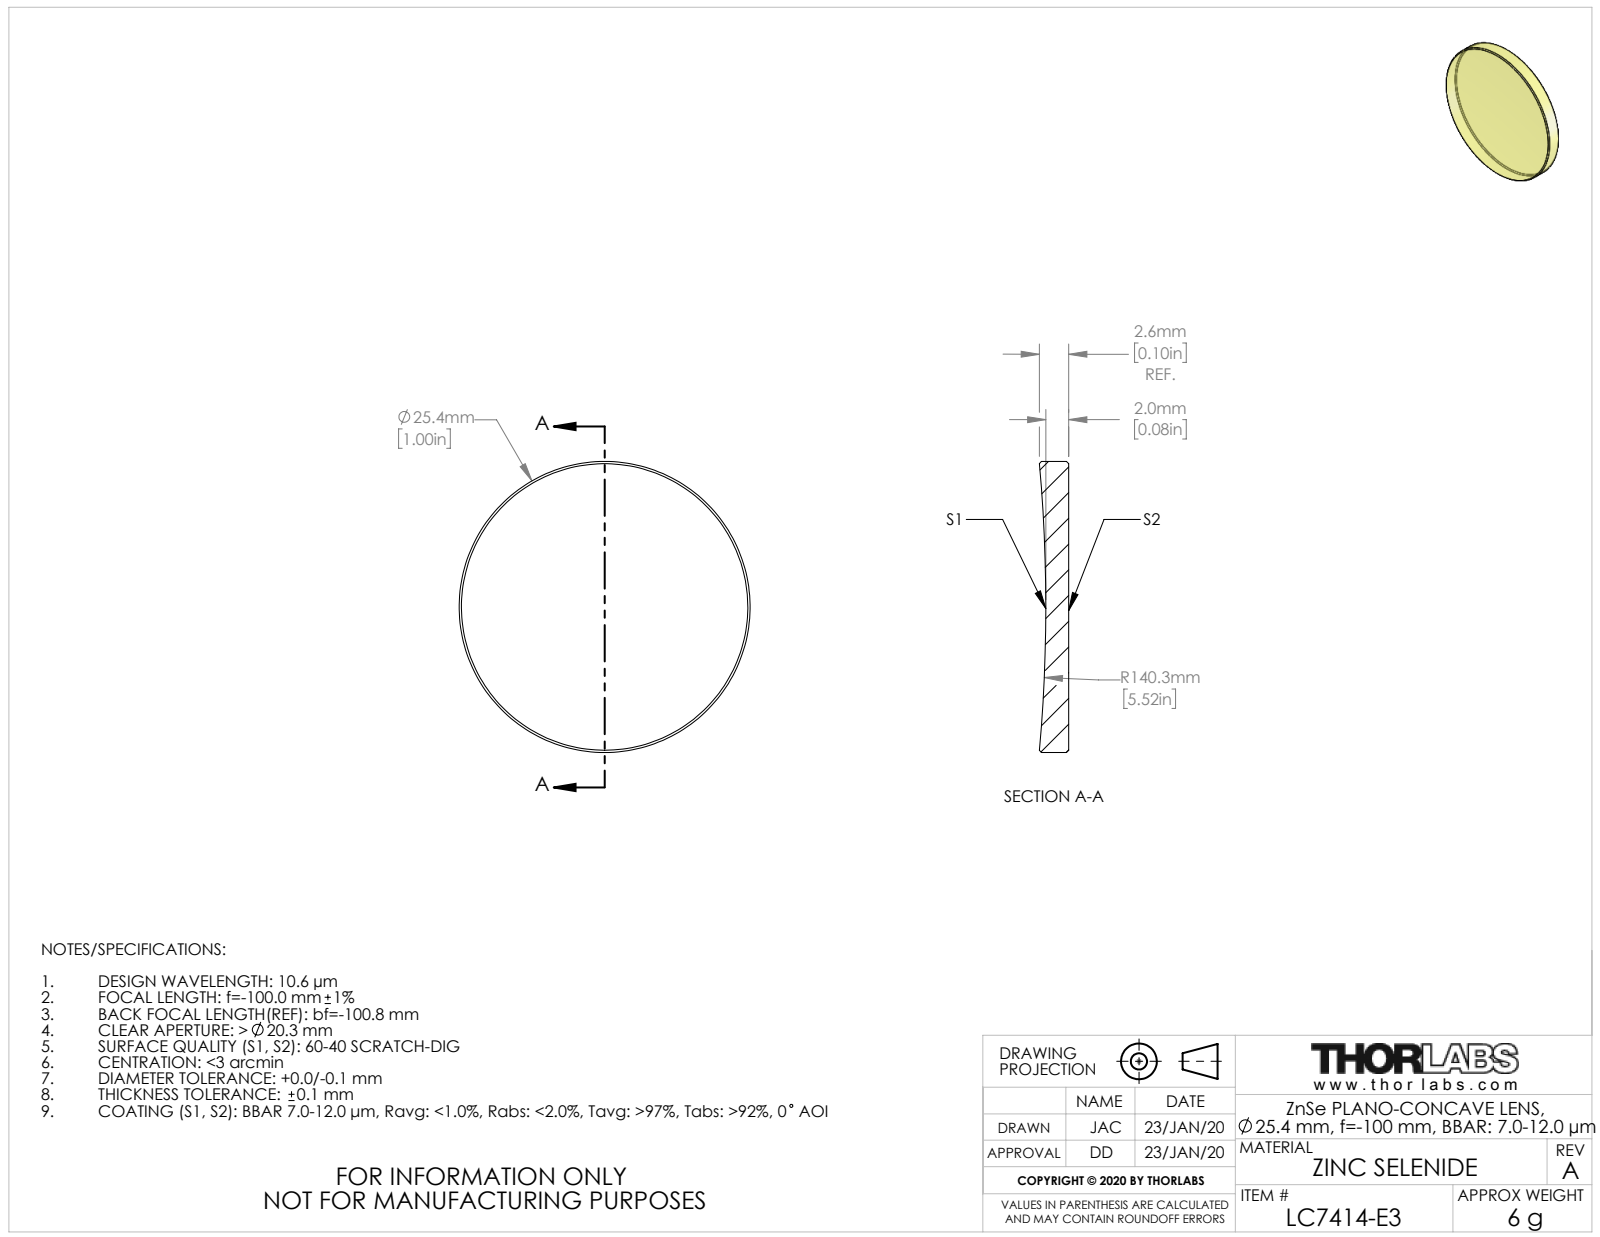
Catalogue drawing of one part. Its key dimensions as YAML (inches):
part_name: "TTN206861-E0W"
step_written_by: "SolidWorks 2018 (CONFIG_CONTROL_DESIGN)"
units: inches
bodies: {solids: 1, faces: 9, planar: 1, cylindrical: 2, other: 6}
overall_size: [1, 1, 0.101]
volume: 0.071
surface_area: 1.86
round_bosses_or_shafts:
  - {diameter: 1, count: 1}
